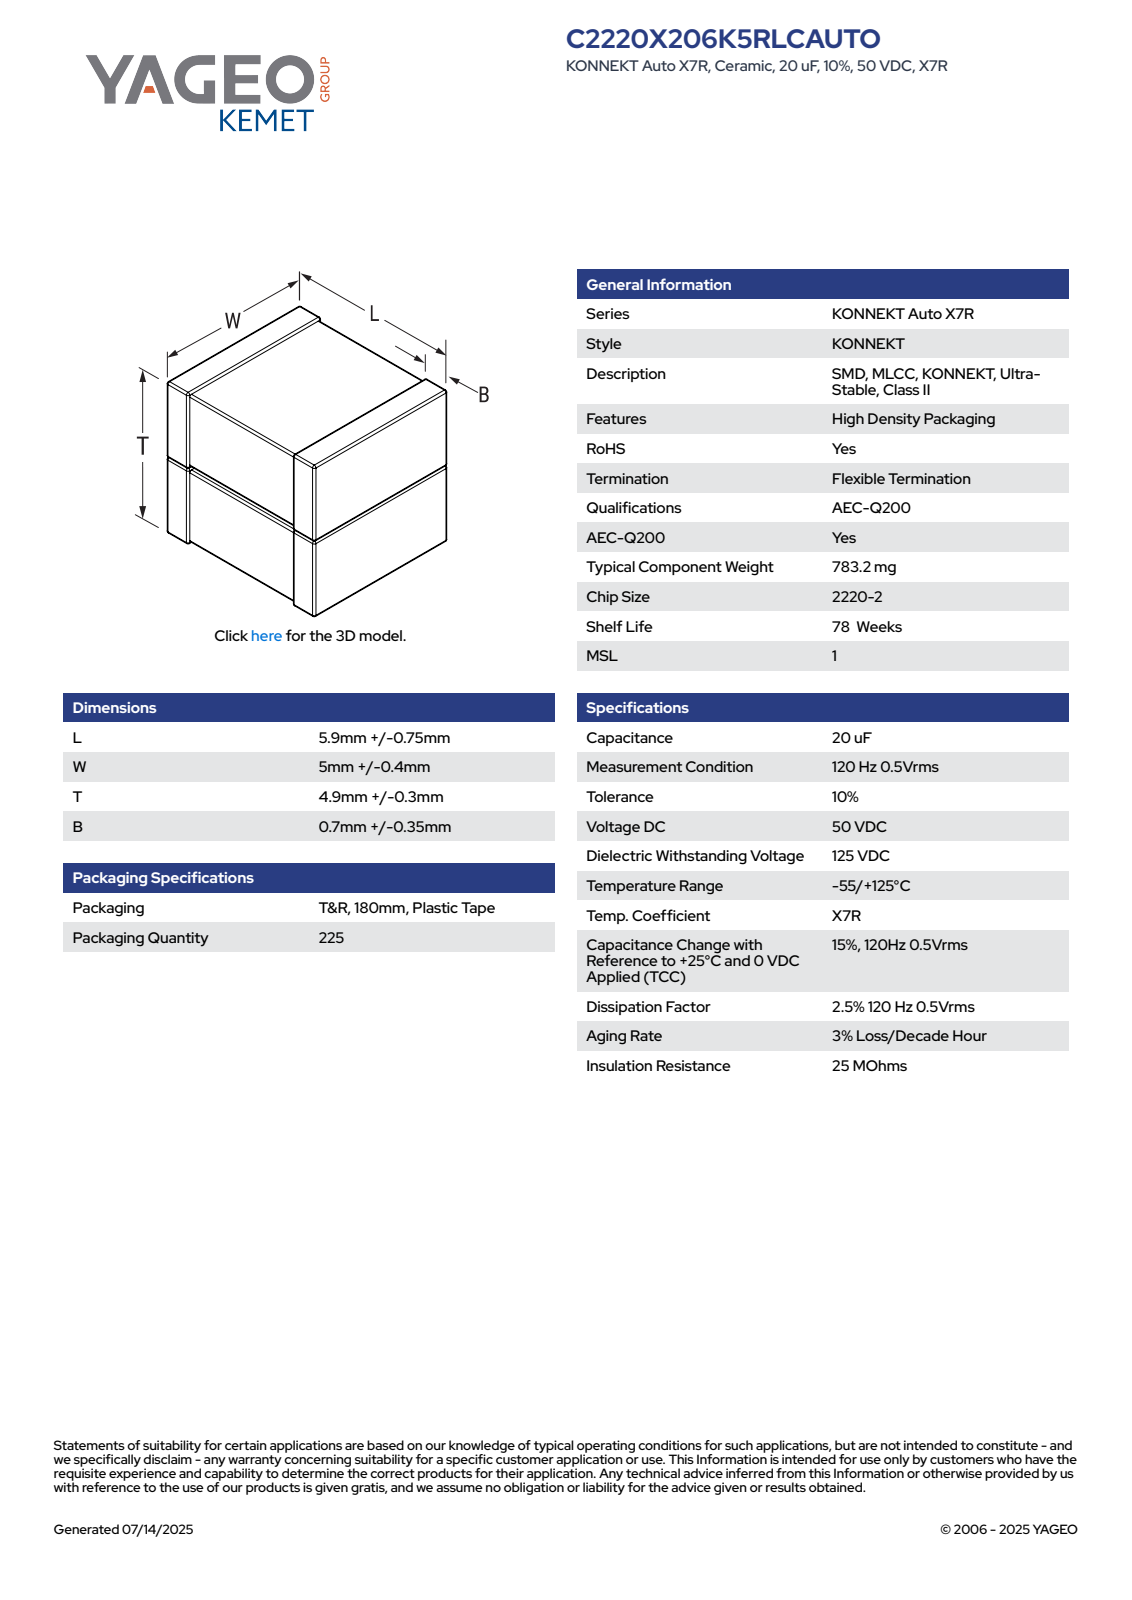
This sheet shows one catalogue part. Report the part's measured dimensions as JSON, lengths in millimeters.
{"part_name": "CCSS_K2T_2220-2_L6.65W5.4B1.05T5.2", "step_written_by": "SolidWorks 2020 (AUTOMOTIVE_DESIGN)", "units": "millimeters", "bodies": {"solids": 4, "faces": 189, "planar": 81, "cylindrical": 76, "other": 32}, "overall_size": [6.65, 5.4, 5.2], "volume_mm3": 177, "surface_area_mm2": 246, "face_to_face_distances": [2.46, 2.6, 6.65, 5.06, 5.26, 2.53, 2.67, 5.13, 5.33, 5.2]}
